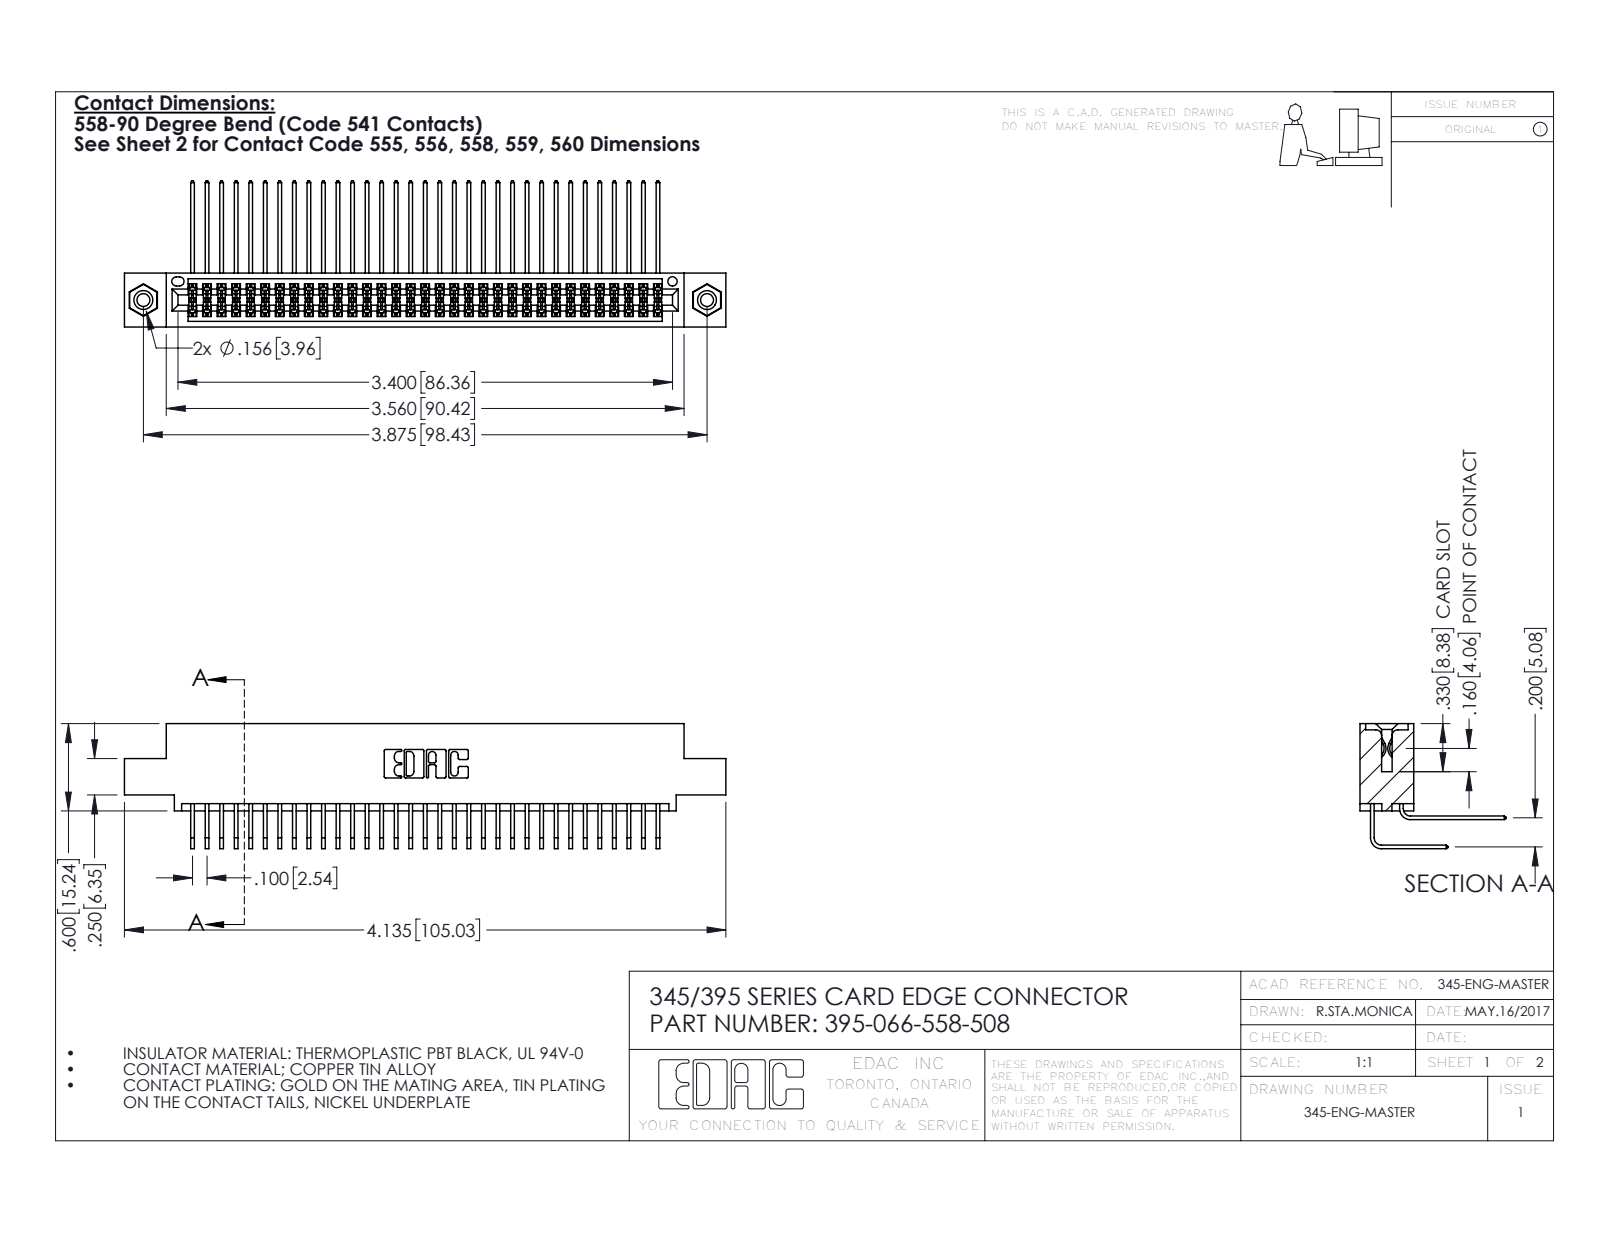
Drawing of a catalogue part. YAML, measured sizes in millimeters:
part_name: "345-292-001_558 559 Tail - 1; 345 Part_0.110 Offset - 0.156 Dia-TI; 395-066-558-508; 345-250-001_345-250-003-102 (+1 more)"
step_written_by: "SolidWorks 2016 (CONFIG_CONTROL_DESIGN)"
units: millimeters
bodies: {solids: 69, faces: 3622, planar: 2426, cylindrical: 1180, other: 16}
overall_size: [105, 25.5, 21.8]
volume: 10400
surface_area: 17120
round_holes:
  - {diameter: 2.3, count: 2}
  - {diameter: 3.2, count: 2}
  - {diameter: 4, count: 2}
  - {diameter: 1.6, count: 1}
round_bosses_or_shafts:
  - {diameter: 3.9, count: 2}
partial_cylinders:
  - {radius: 0.2, count: 100}
  - {radius: 0.3, count: 22}
  - {radius: 0.2, count: 6}
  - {radius: 0.8, count: 6}
  - {radius: 0.7, count: 3}
  - {radius: 0.4, count: 2}
  - {radius: 0.5, count: 2}
  - {radius: 0.6, count: 2}
face_to_face_distances: [1.8, 7.6, 5.1, 9.4, 2.5, 6.9, 0.6, 5.7, 0.6, 4.4]
hole_center_spacings: [6.9, 92.5, 98.4]
